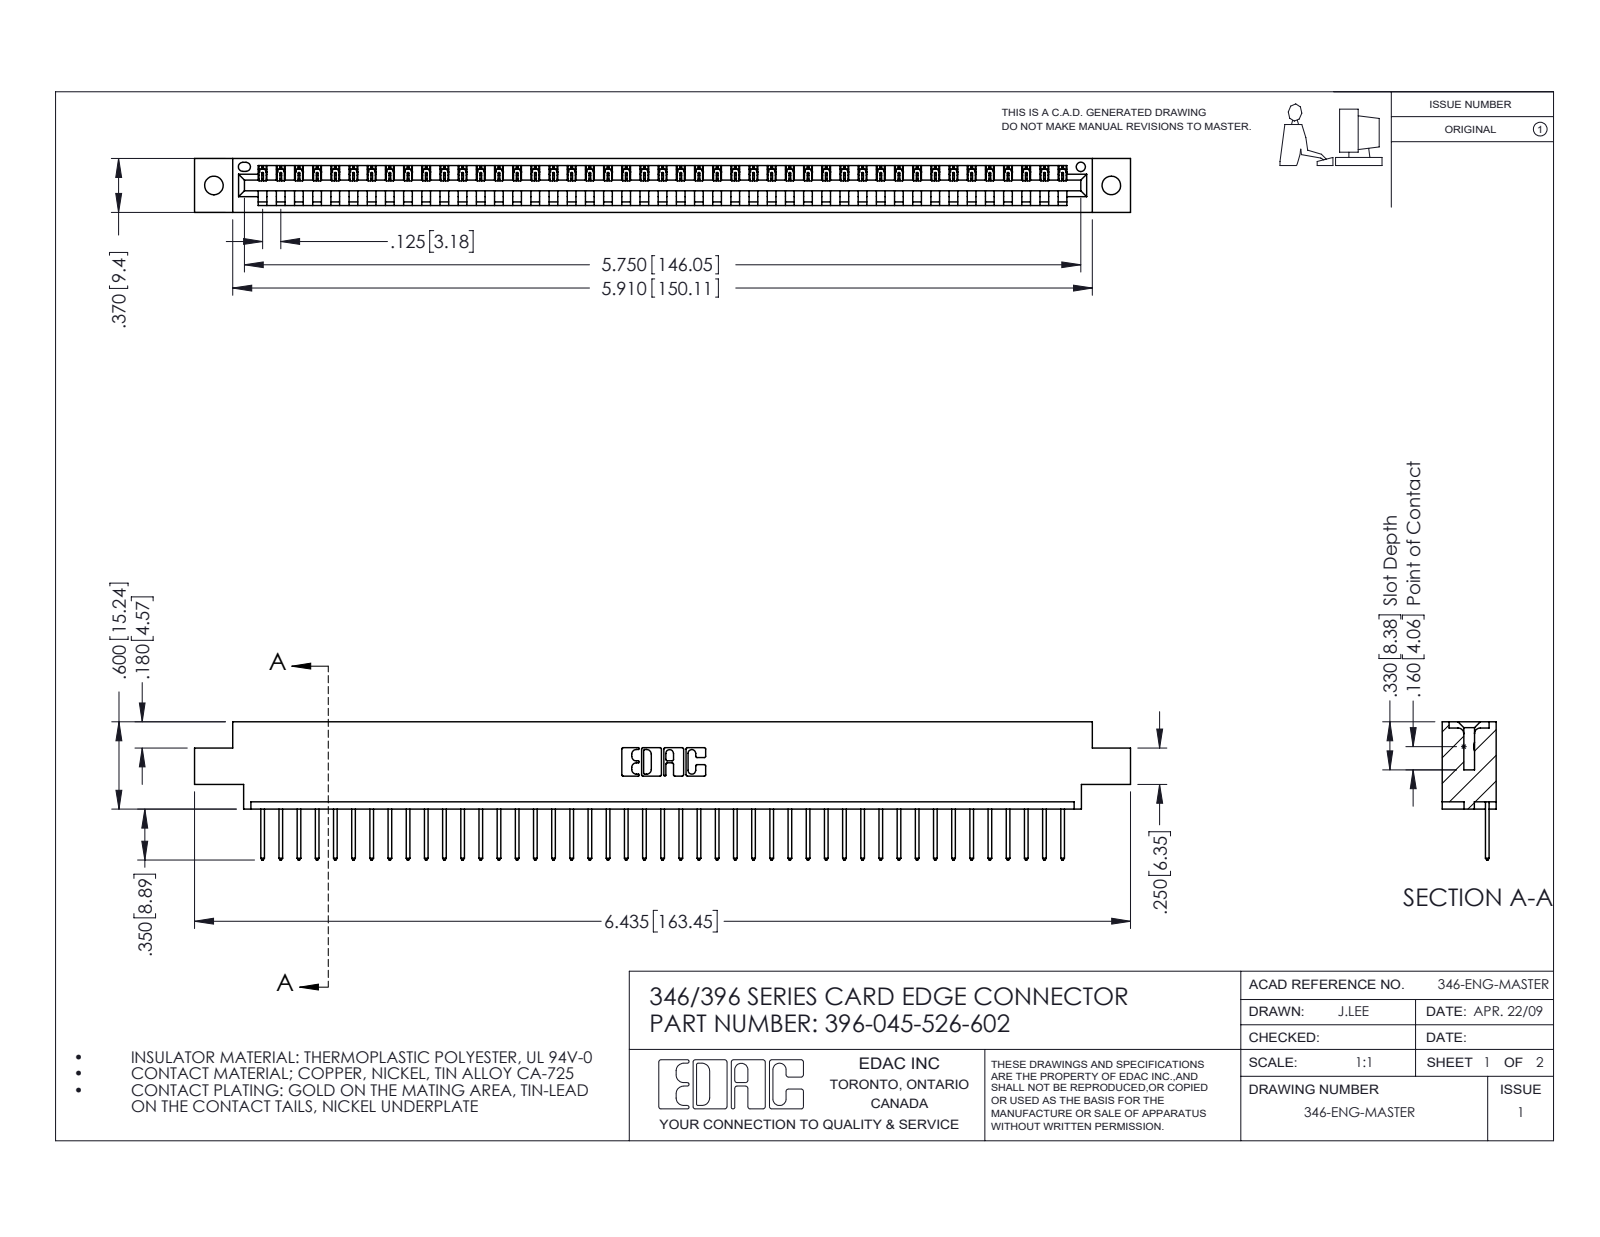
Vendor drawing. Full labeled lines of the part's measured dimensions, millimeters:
Part name (STEP PRODUCT): 396-045-526-602; 346 Part_0.170 Offset - 0.128 Dia; 345-292-001_345-293-126
STEP written by: SolidWorks 2016 (CONFIG_CONTROL_DESIGN)
Units: millimetres
Bodies: 46 solids, 2736 faces (1880 planar, 856 cylindrical, 0 other)
Overall size (bounding box): 163.4 × 24.1 × 9.4
Volume: 15 400 mm³ · Surface area: 19 170 mm²
Round holes (diameter × count): ⌀3.3 ×2, ⌀1.6 ×1
Partial cylindrical surfaces — rounded edges, fillets, slot ends (radius × count): R0.2 ×90, R0.3 ×90, R0.3 ×22, R0.2 ×6, R0.8 ×6, R0.7 ×3, R0.8 ×2, R1 ×2
Main face-to-face distances: 1.2, 8.2, 9.4, 6.4, 1.8, 7.6, 0.6, 3.8, 5.6, 2.5
Hole centre spacings: 6.2, 151.4, 156.7
